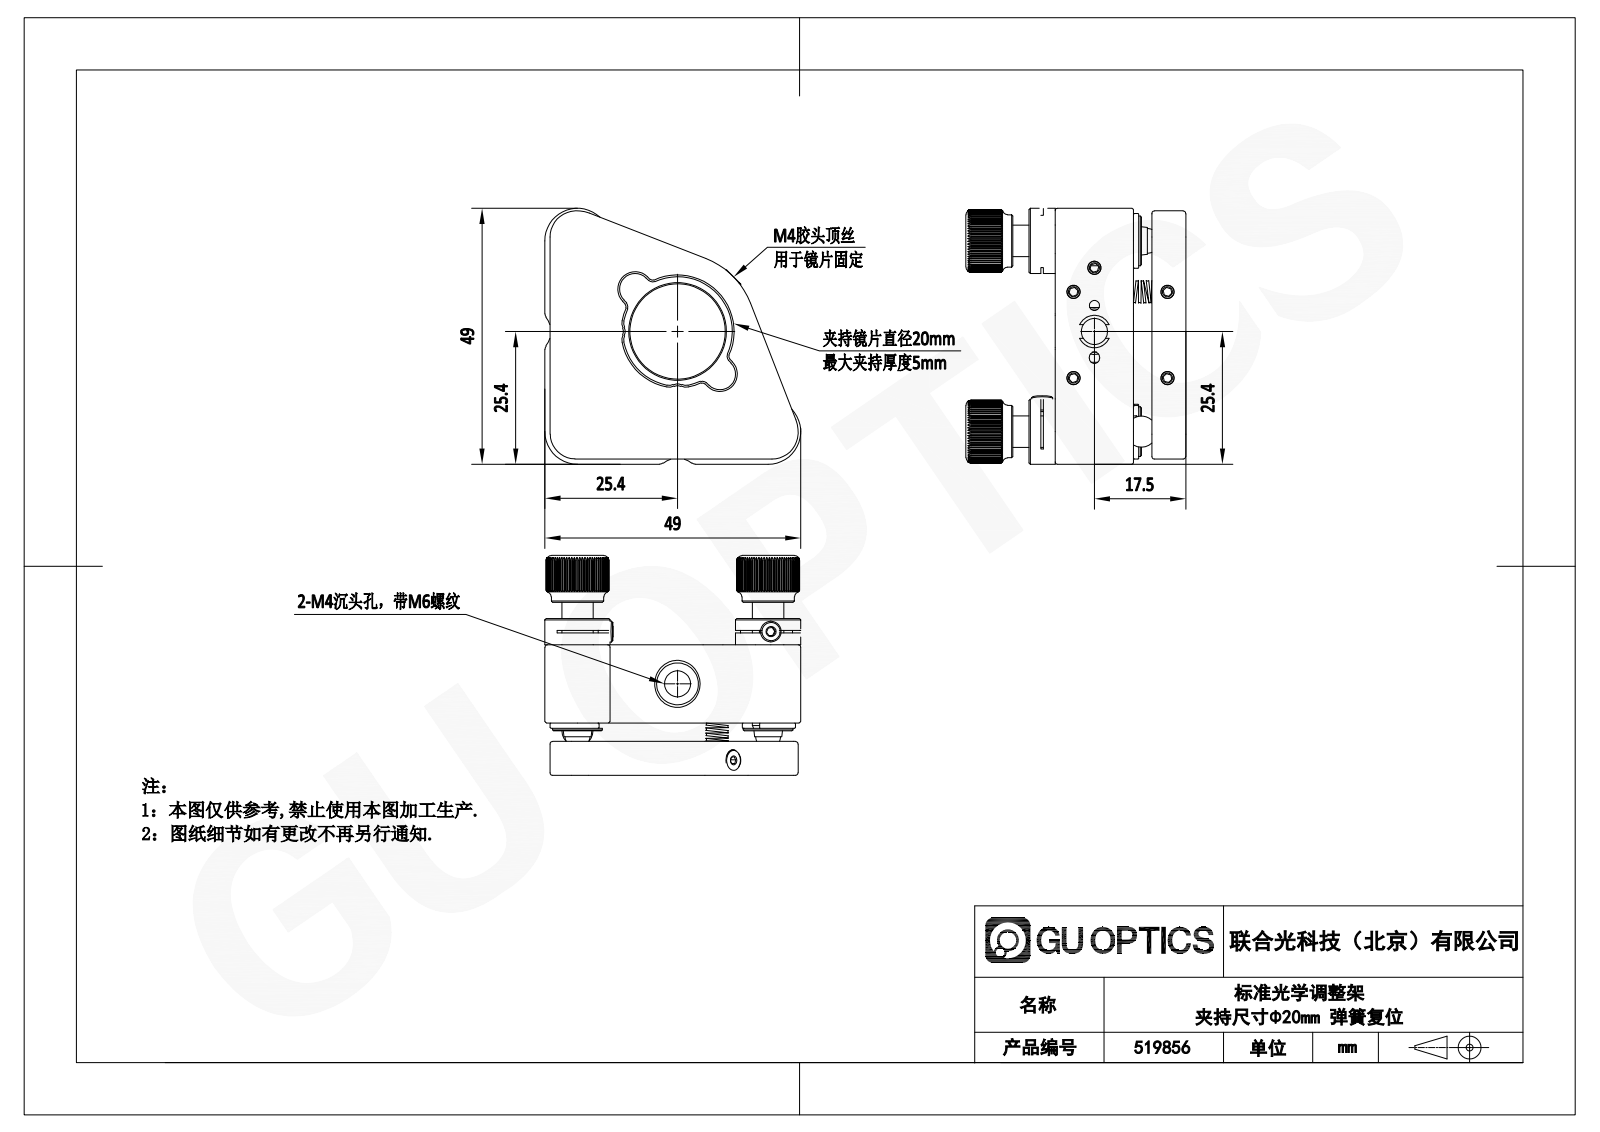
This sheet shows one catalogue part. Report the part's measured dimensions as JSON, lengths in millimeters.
{"part_name": "519856", "step_written_by": "SolidWorks 2020 (CONFIG_CONTROL_DESIGN)", "units": "millimeters", "bodies": {"solids": 0, "faces": 858, "planar": 456, "cylindrical": 265, "other": 137}, "overall_size": [49, 49, 42.1], "round_holes": [[6, 4], [2, 2], [5, 2], [8, 2], [10, 2], [9.5, 1]], "round_bosses_or_shafts": [[3, 8], [4, 5], [1.5, 4], [12.5, 2], [6, 2], [4.6, 2], [18.3, 1], [9.5, 1]], "partial_cylinders_radius": [[0.5, 12], [1, 12], [0.8, 8], [2, 6], [0.3, 5], [6.25, 3], [3, 2], [3.1, 2]], "face_to_face_distances": [6.5, 18.5, 25, 3.5, 10, 15, 1, 2.25, 2.75, 11.5], "hole_center_spacings": [5, 9.75, 16.5, 26.25, 28.65, 37.91, 45.25, 14.5]}
